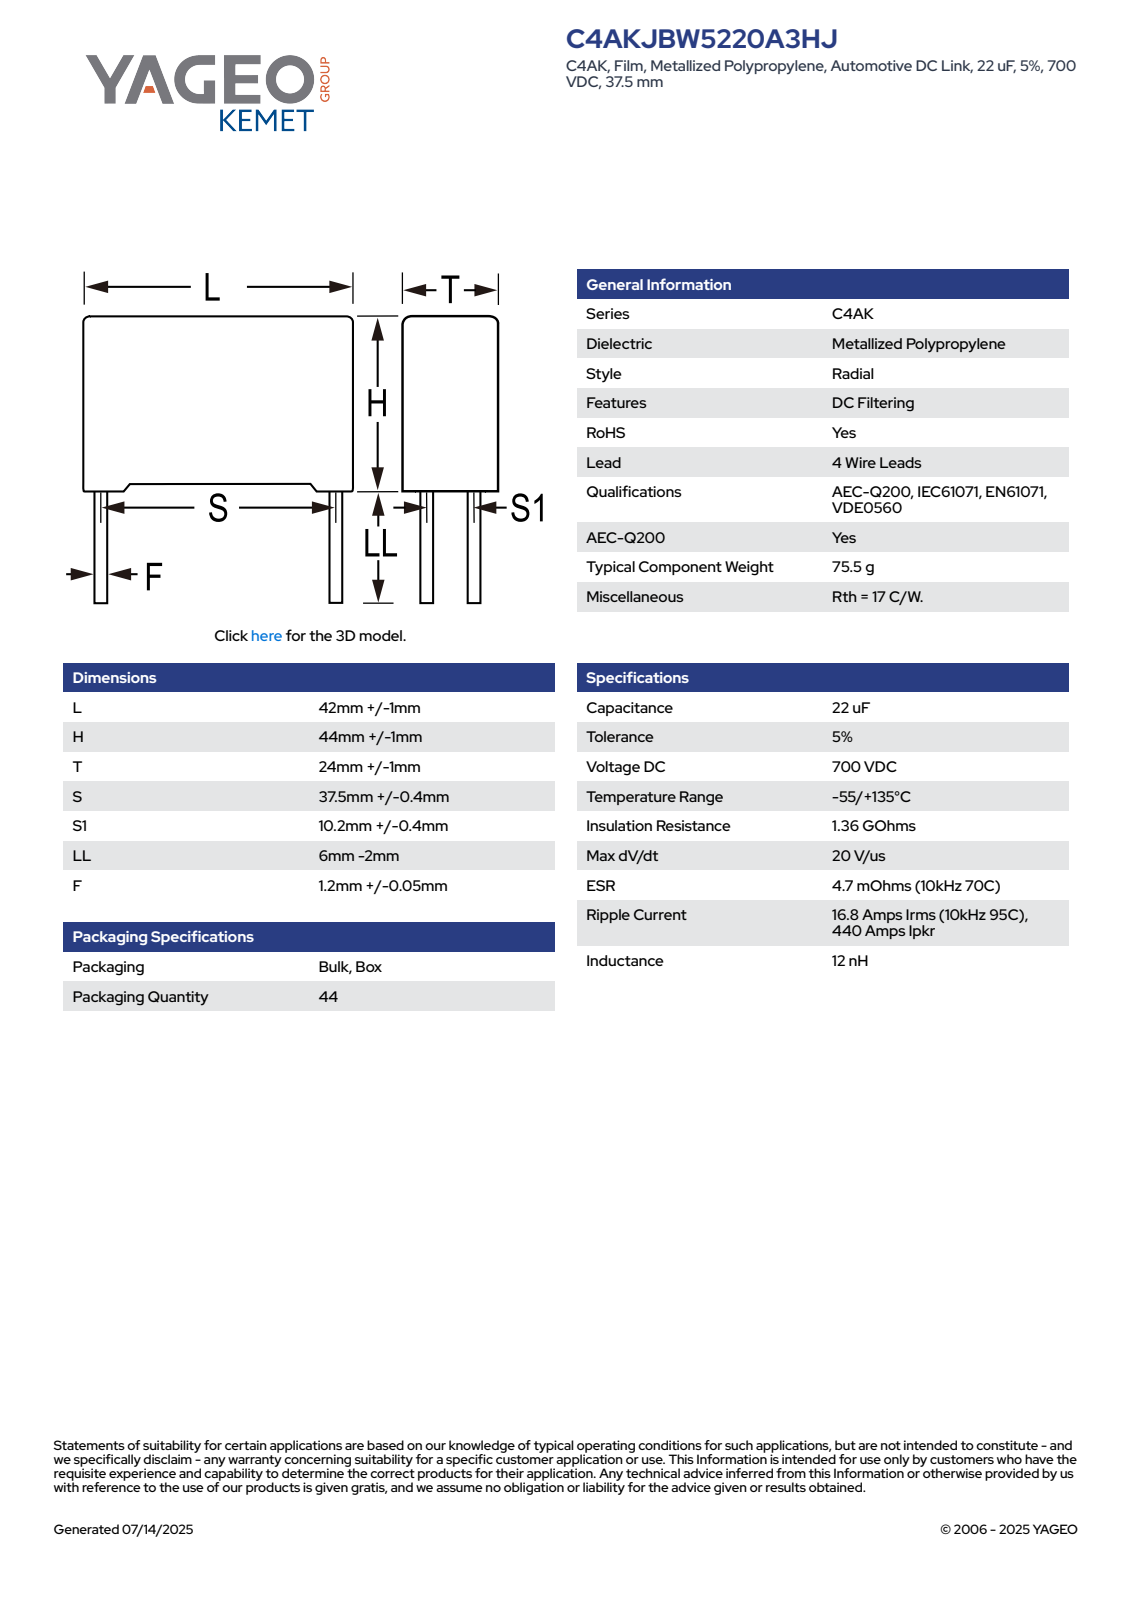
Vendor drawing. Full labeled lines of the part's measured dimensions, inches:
Part name (STEP PRODUCT): CFP_RB4_42X44X24_L43H45T25S37.5S110.2LL4F1.25
STEP written by: SolidWorks 2014 (AUTOMOTIVE_DESIGN)
Units: inches
Bodies: 4 solids, 87 faces (79 planar, 8 cylindrical, 0 other)
Overall size (bounding box): 1.929 × 1.693 × 0.984
Volume: 2.876 in³ · Surface area: 13.17 in²
Round bosses / shafts (diameter × count): ⌀0.049 ×4
Main face-to-face distances: 0.984, 1.693, 1.72, 0.052, 1.772, 0.061, 0.985, 1.632, 0.924, 1.572
